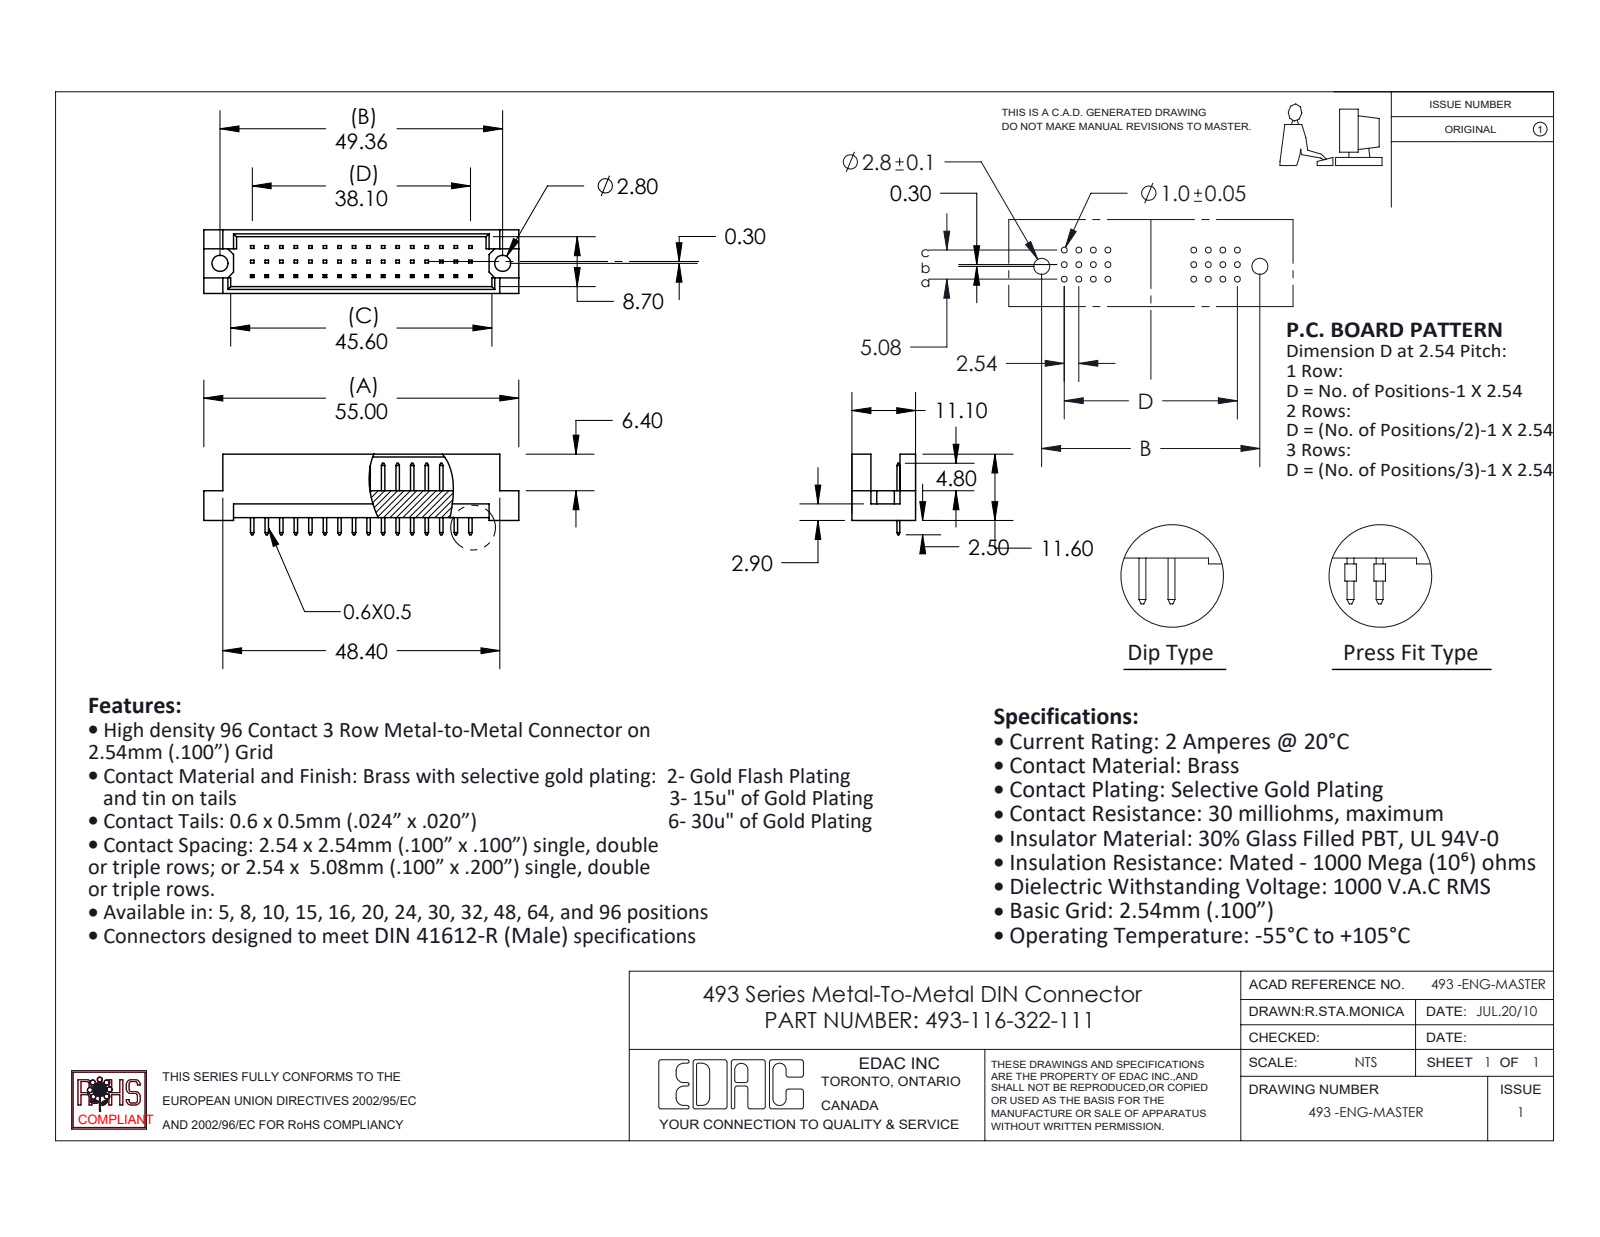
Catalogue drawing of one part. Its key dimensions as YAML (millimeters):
part_name: "493 Part_48; 493-116-322-112; 493-290_22"
step_written_by: "SolidWorks 2020 (CONFIG_CONTROL_DESIGN)"
units: millimeters
bodies: {solids: 17, faces: 468, planar: 464, cylindrical: 4, other: 0}
overall_size: [55, 14.1, 11.1]
volume: 3331
surface_area: 4190
round_holes:
  - {diameter: 2.8, count: 2}
face_to_face_distances: [1.2, 9.9, 11.1, 8.7, 4.7, 0.5, 2.54, 5.08, 2.76, 8.34]
hole_center_spacings: [49.36]
